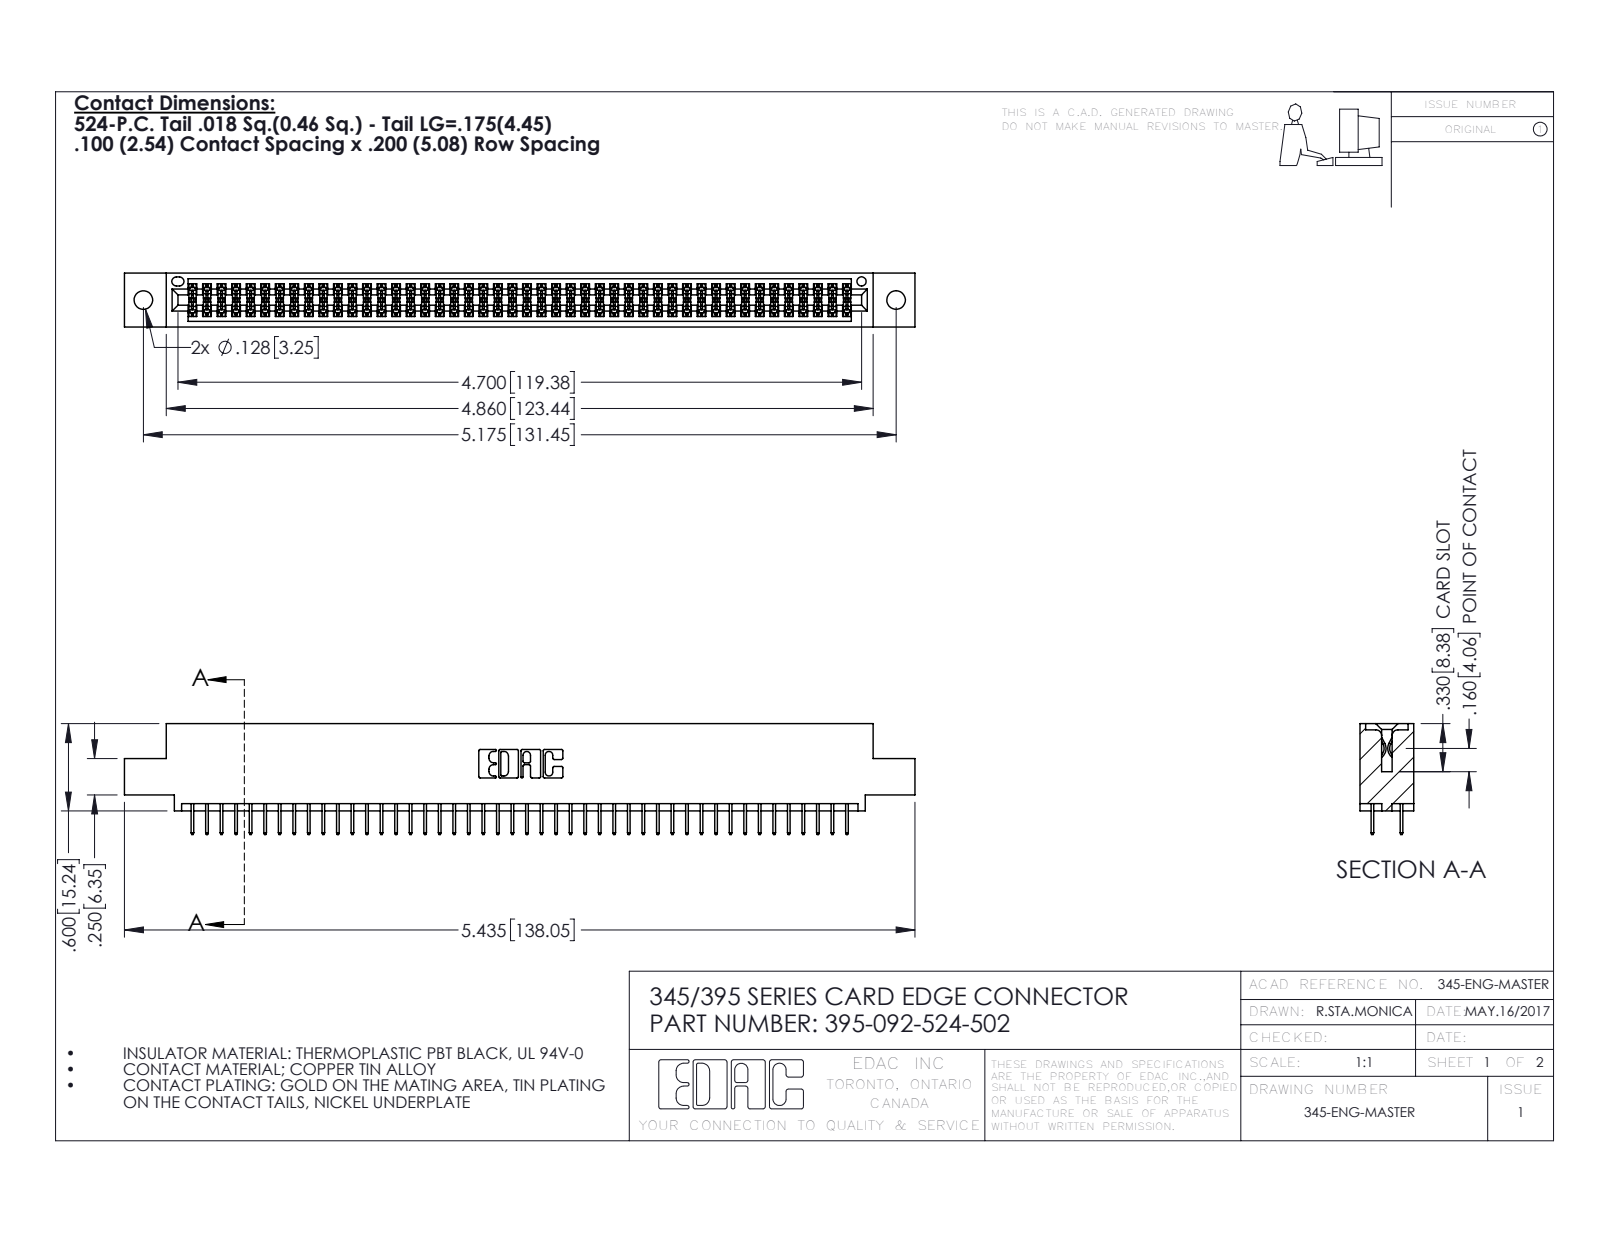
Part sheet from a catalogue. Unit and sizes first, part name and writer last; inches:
Units: inches
Overall size (bounding box): 5.435 × 0.762 × 0.37
Round holes (diameter × count): ⌀0.128 ×2, ⌀0.064 ×1
Partial cylindrical surfaces — rounded edges, fillets, slot ends (radius × count): R0.006 ×138, R0.01 ×22, R0.007 ×6, R0.031 ×6, R0.026 ×3, R0.014 ×2, R0.019 ×2, R0.022 ×2
Main face-to-face distances: 0.072, 0.298, 0.2, 0.37, 0.098, 0.272, 0.025, 0.225, 0.072, 0.175
Hole centre spacings: 0.27, 4.939, 5.175
Volume: 0.805 in³ · Surface area: 29.51 in²
Bodies: 93 solids, 5098 faces (3672 planar, 1426 cylindrical, 0 other)
Part name (STEP PRODUCT): 395-092-524-502; 345-292-001_345-293-124; 345 Part_0.110 Offset - 0.128 Dia
STEP written by: SolidWorks 2016 (CONFIG_CONTROL_DESIGN)
